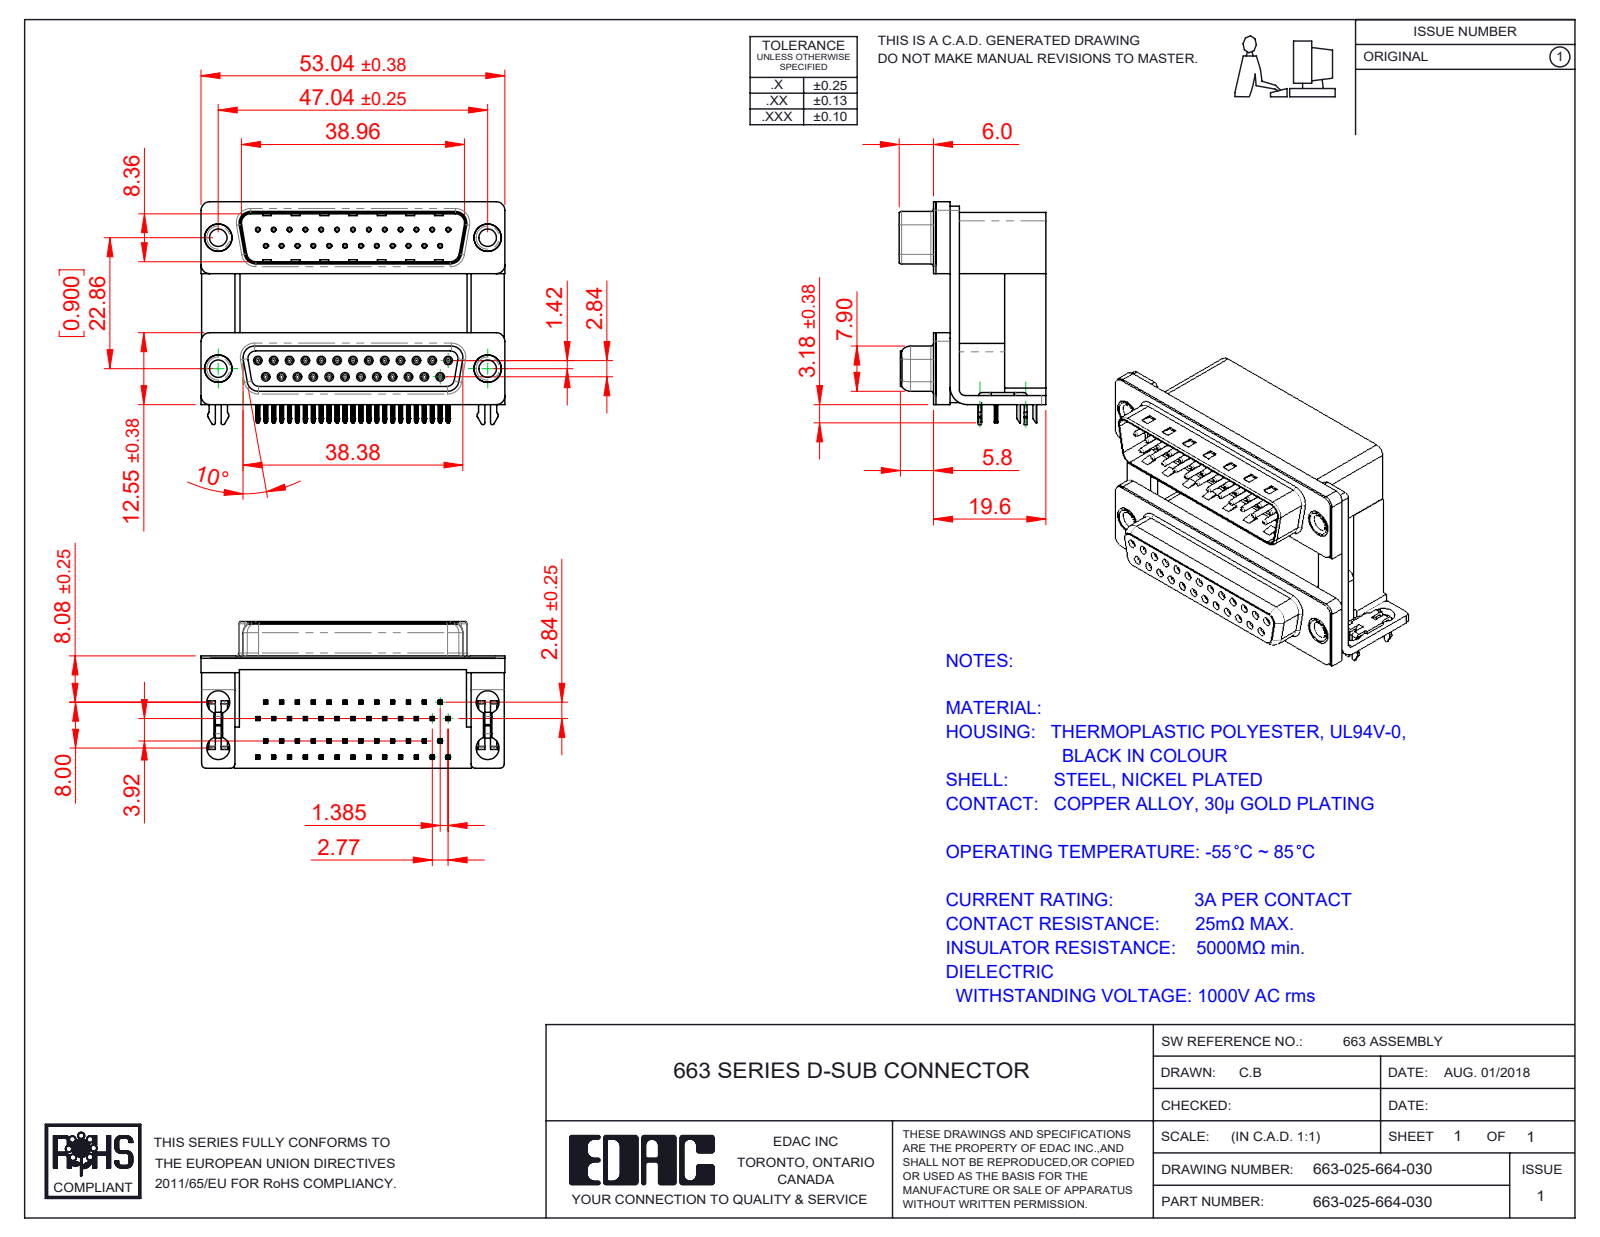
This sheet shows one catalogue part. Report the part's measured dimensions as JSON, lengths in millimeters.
{"part_name": "663 Mounting Bracket_2ProngH; 663 Housing Upper_25 Contacts H; 663 Thru Hole Rivet; 663 Shell Receptacle_25 Contacts (+8 more)", "step_written_by": "SolidWorks 2020 (CONFIG_CONTROL_DESIGN)", "units": "millimeters", "bodies": {"solids": 63, "faces": 6271, "planar": 3359, "cylindrical": 1557, "other": 1355}, "overall_size": [53.04, 38.91, 25.6], "volume_mm3": 23695, "surface_area_mm2": 25132, "round_holes": [[0.8, 50], [0.35, 25], [0.9, 25], [4, 8], [3.05, 4], [3.5, 4], [4.8, 4], [5, 4]], "round_bosses_or_shafts": [[1.2, 25], [0.75, 25], [4.9, 4], [4.75, 4], [3.85, 4]], "partial_cylinders_radius": [[0.1, 202], [0.25, 110], [0.15, 100], [0.12, 50], [0.35, 50], [0.34, 25], [0.5, 16], [1.5, 14]], "face_to_face_distances": [19.2, 12, 7.2, 0.4, 10.7, 16.7, 9.5, 2.5, 22.86, 12.4], "hole_center_spacings": [3.16, 2.77, 5.54, 11.08, 8.31, 5.03, 13.85, 7.48]}
